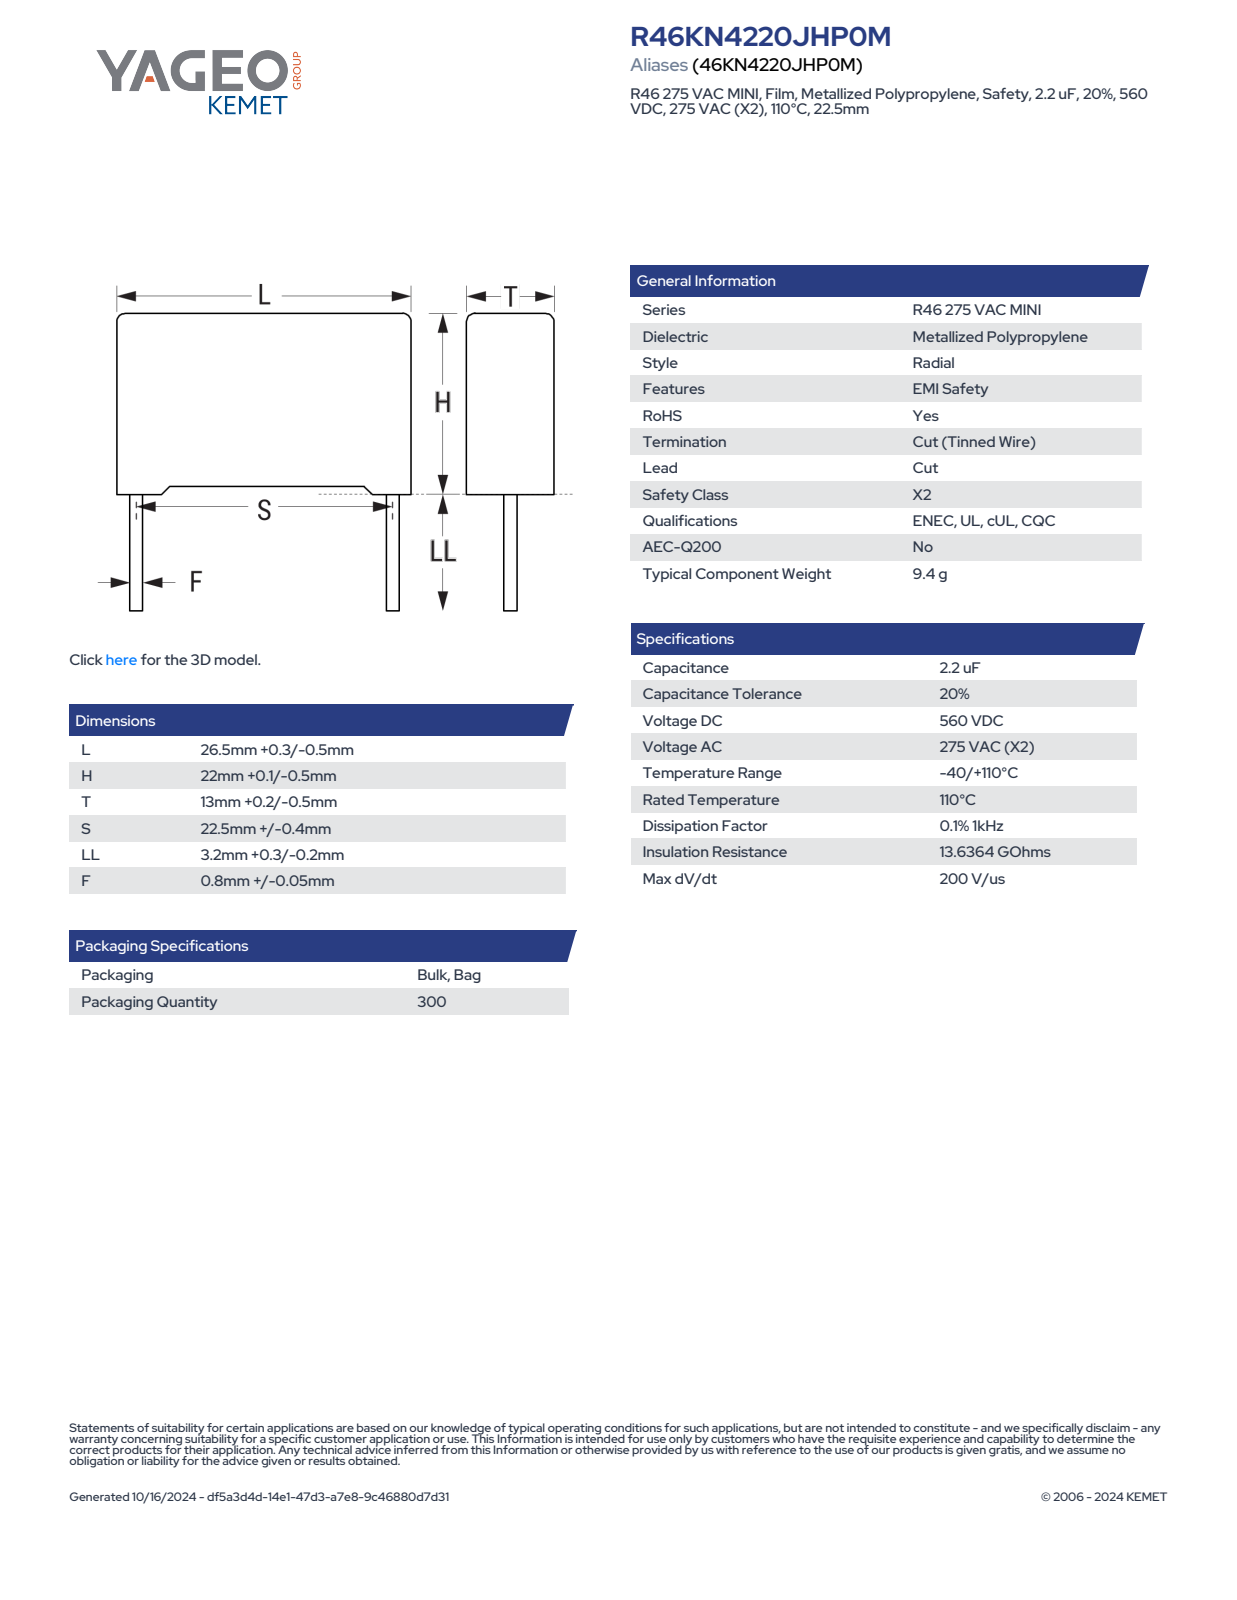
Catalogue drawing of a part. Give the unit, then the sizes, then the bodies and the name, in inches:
Units: inches
Overall size (bounding box): 1.055 × 1.008 × 0.52
Round bosses / shafts (diameter × count): ⌀0.033 ×2
Partial cylindrical surfaces — rounded edges, fillets, slot ends (radius × count): R0.02 ×4
Main face-to-face distances: 0.52, 1.055, 0.84, 0.841, 0.03, 0.03, 0.87, 0.035, 1.02, 0.52
Volume: 0.462 in³ · Surface area: 3.928 in²
Bodies: 4 solids, 85 faces (77 planar, 8 cylindrical, 0 other)
Part name (STEP PRODUCT): CFR_RB2_26.5X22X13_L26.8H22.1T13.2S22.5LL3.5F0.85
STEP written by: SolidWorks 2021 (AUTOMOTIVE_DESIGN)
